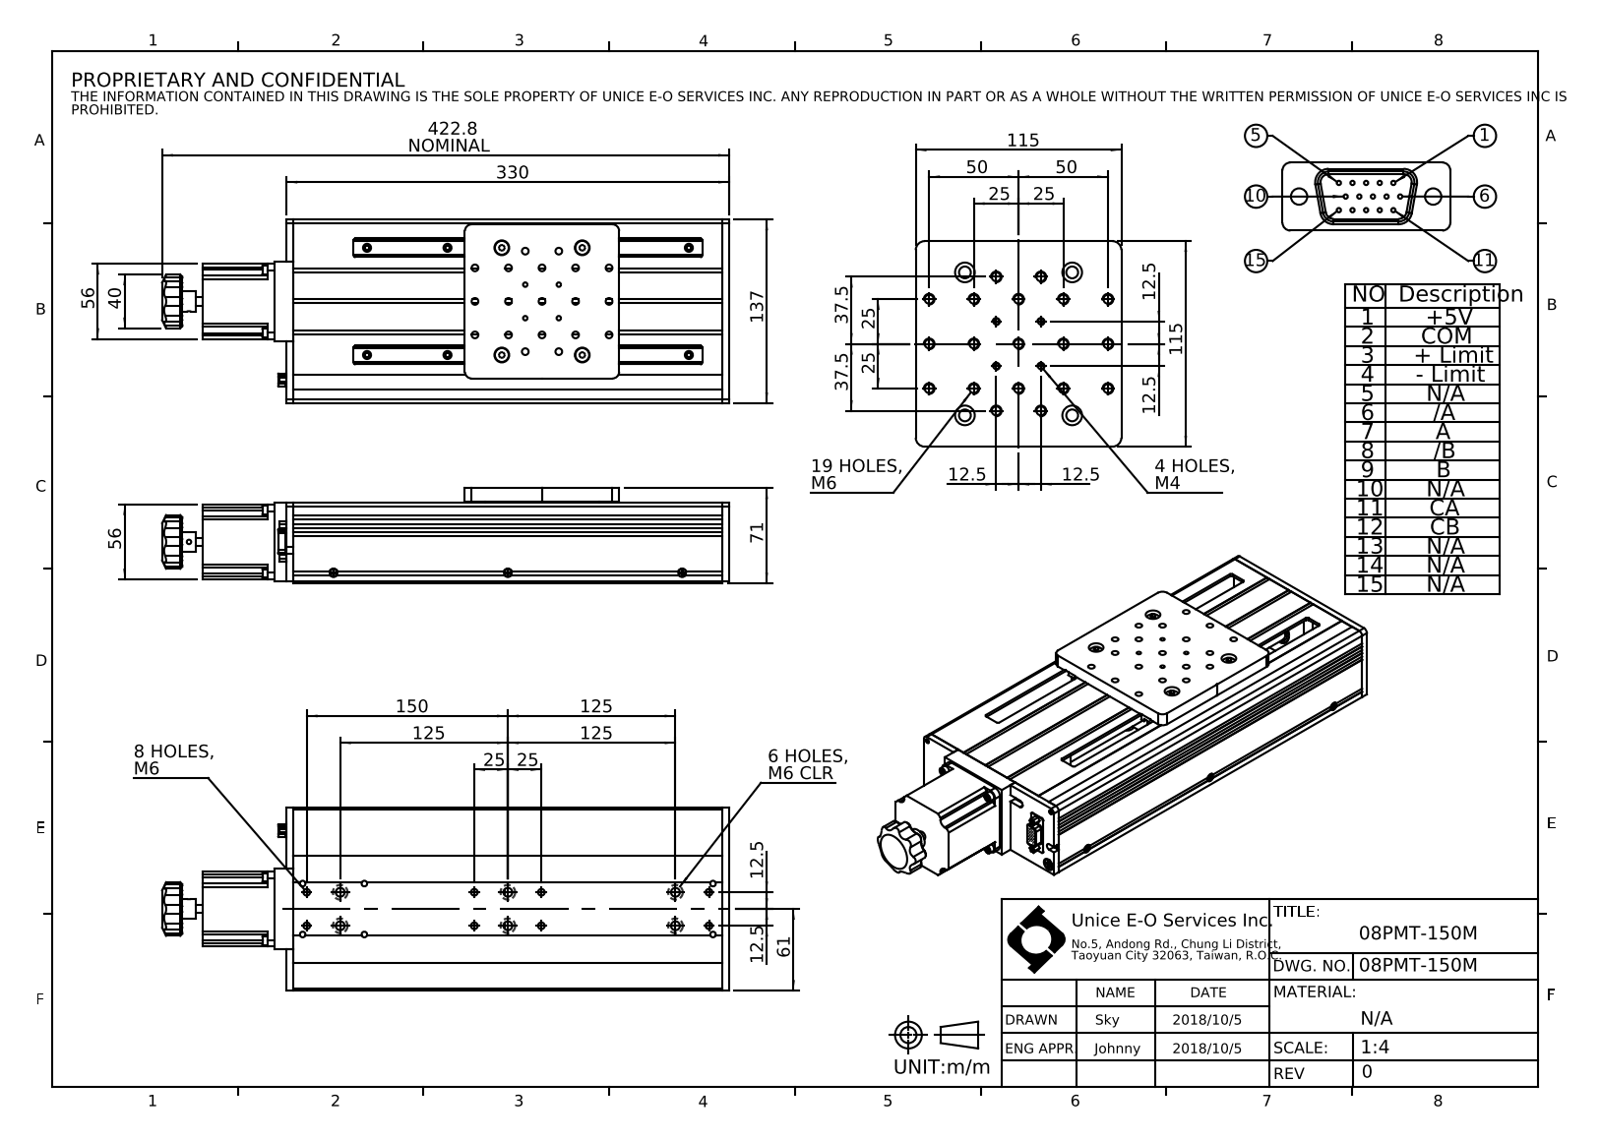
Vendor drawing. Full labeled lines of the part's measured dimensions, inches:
Part name (STEP PRODUCT): 08PMT-150M
STEP written by: SolidWorks 2016 (AUTOMOTIVE_DESIGN)
Units: inches
Bodies: 0 solids, 760 faces (370 planar, 265 cylindrical, 125 other)
Overall size (bounding box): 16.646 × 5.394 × 2.795
Round holes (diameter × count): ⌀0.197 ×27, ⌀0.433 ×10, ⌀0.031 ×6, ⌀0.13 ×6, ⌀0.165 ×6, ⌀0.26 ×6, ⌀0.039 ×3, ⌀0.079 ×2, ⌀0.098 ×2, ⌀0.866 ×1, ⌀1.004 ×1, ⌀1.024 ×1
Round bosses / shafts (diameter × count): ⌀0.256 ×4, ⌀0.228 ×3, ⌀0.118 ×3, ⌀0.303 ×2, ⌀0.78 ×1, ⌀0.756 ×1, ⌀0.63 ×1, ⌀0.591 ×1
Partial cylindrical surfaces — rounded edges, fillets, slot ends (radius × count): R0.059 ×12, R0.157 ×8, R0.197 ×8, R0.276 ×8, R0.02 ×6, R0.079 ×4, R0.177 ×4, R0.118 ×3
Main face-to-face distances: 0.079, 2.382, 5.315, 5.236, 0.413, 0.059, 2.323, 5.394, 0.067, 0.197
Hole centre spacings: 0.984, 1.392, 2.048, 1.118, 4.921, 5.019, 5.906, 5.987
